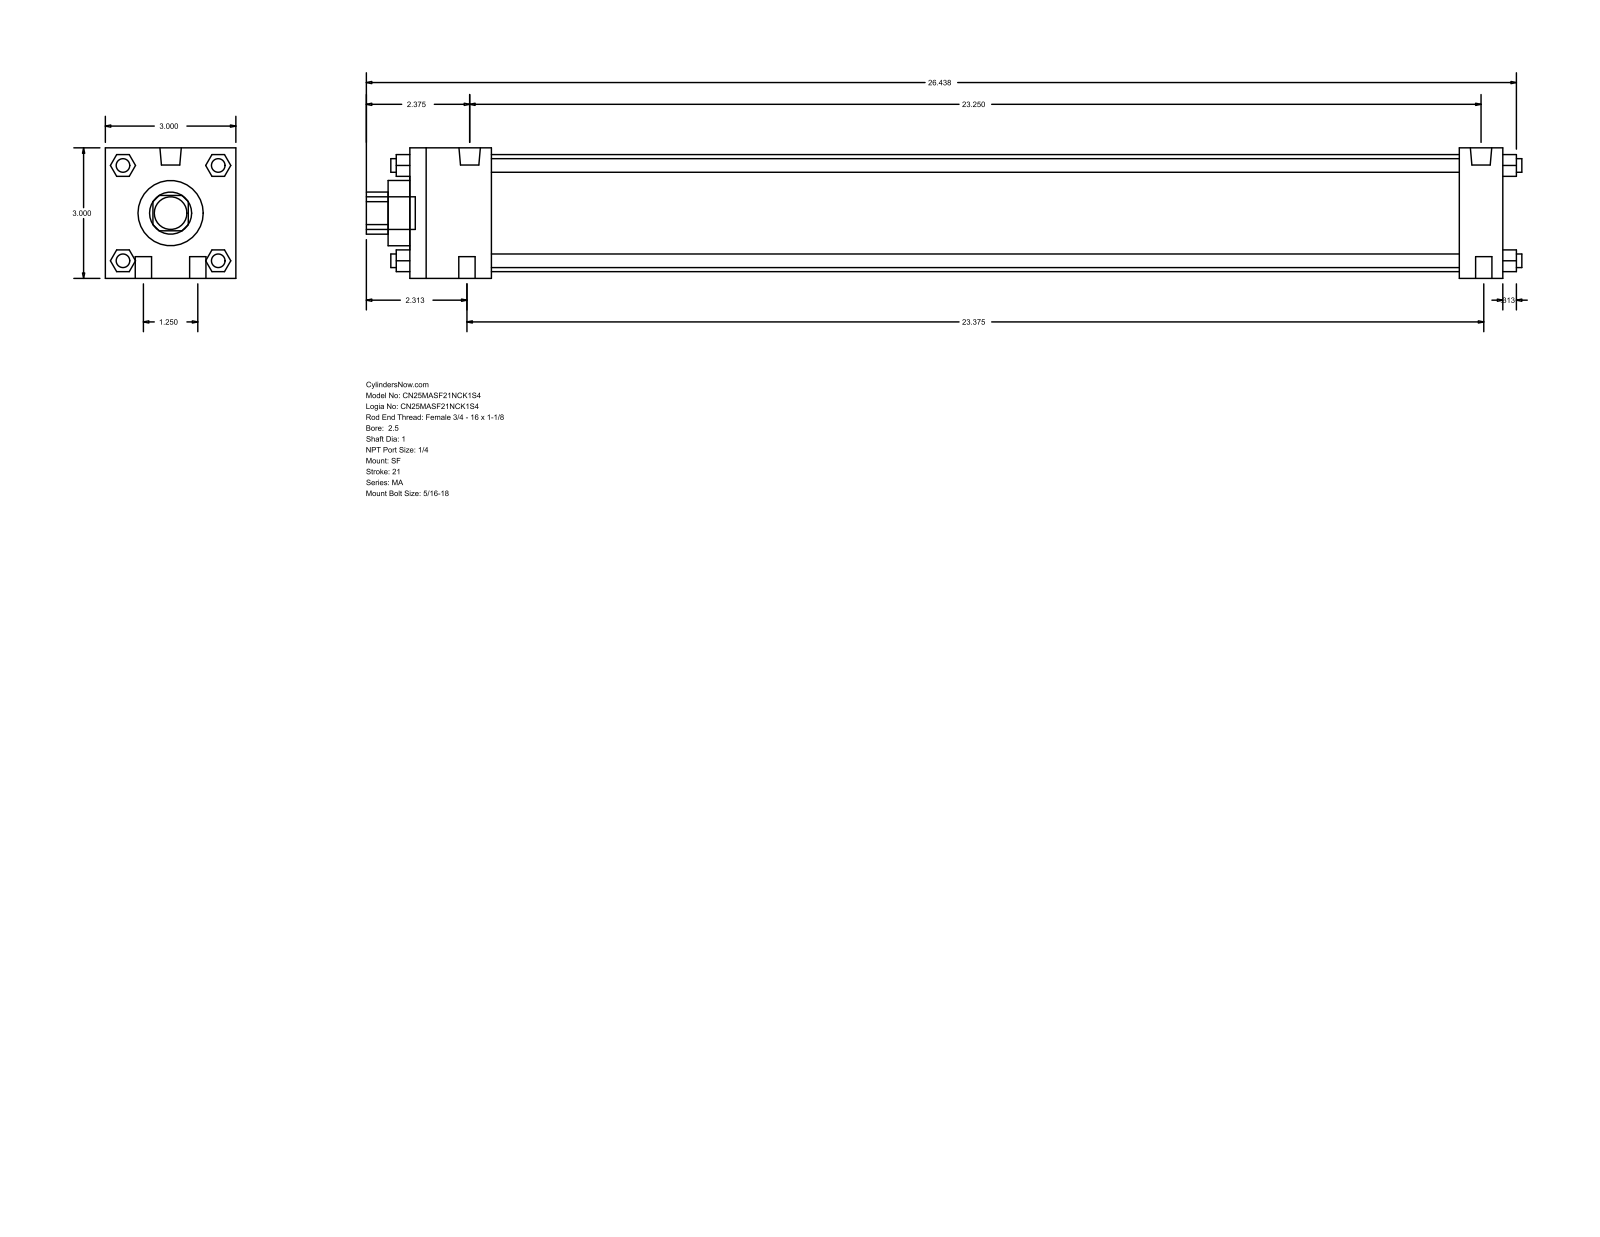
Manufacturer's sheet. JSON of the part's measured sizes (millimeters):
{"part_name": "MA_SF__0250_1", "step_written_by": "GSSL Pune (CONFIG_CONTROL_DESIGN)", "units": "millimeters", "bodies": {"solids": 0, "faces": 124, "planar": 94, "cylindrical": 30, "other": 0}, "overall_size": [674.69, 76.2, 76.2], "round_holes": [[25.4, 1], [38.1, 1], [68.33, 1]], "round_bosses_or_shafts": [[7.94, 6], [9.53, 4], [12.49, 2], [19.05, 1]], "partial_cylinders_radius": [[12.29, 1]], "face_to_face_distances": [76.2, 638.18, 12.7, 612.77, 25.41, 47.63, 565.14, 590.55, 27.81, 48.17]}
